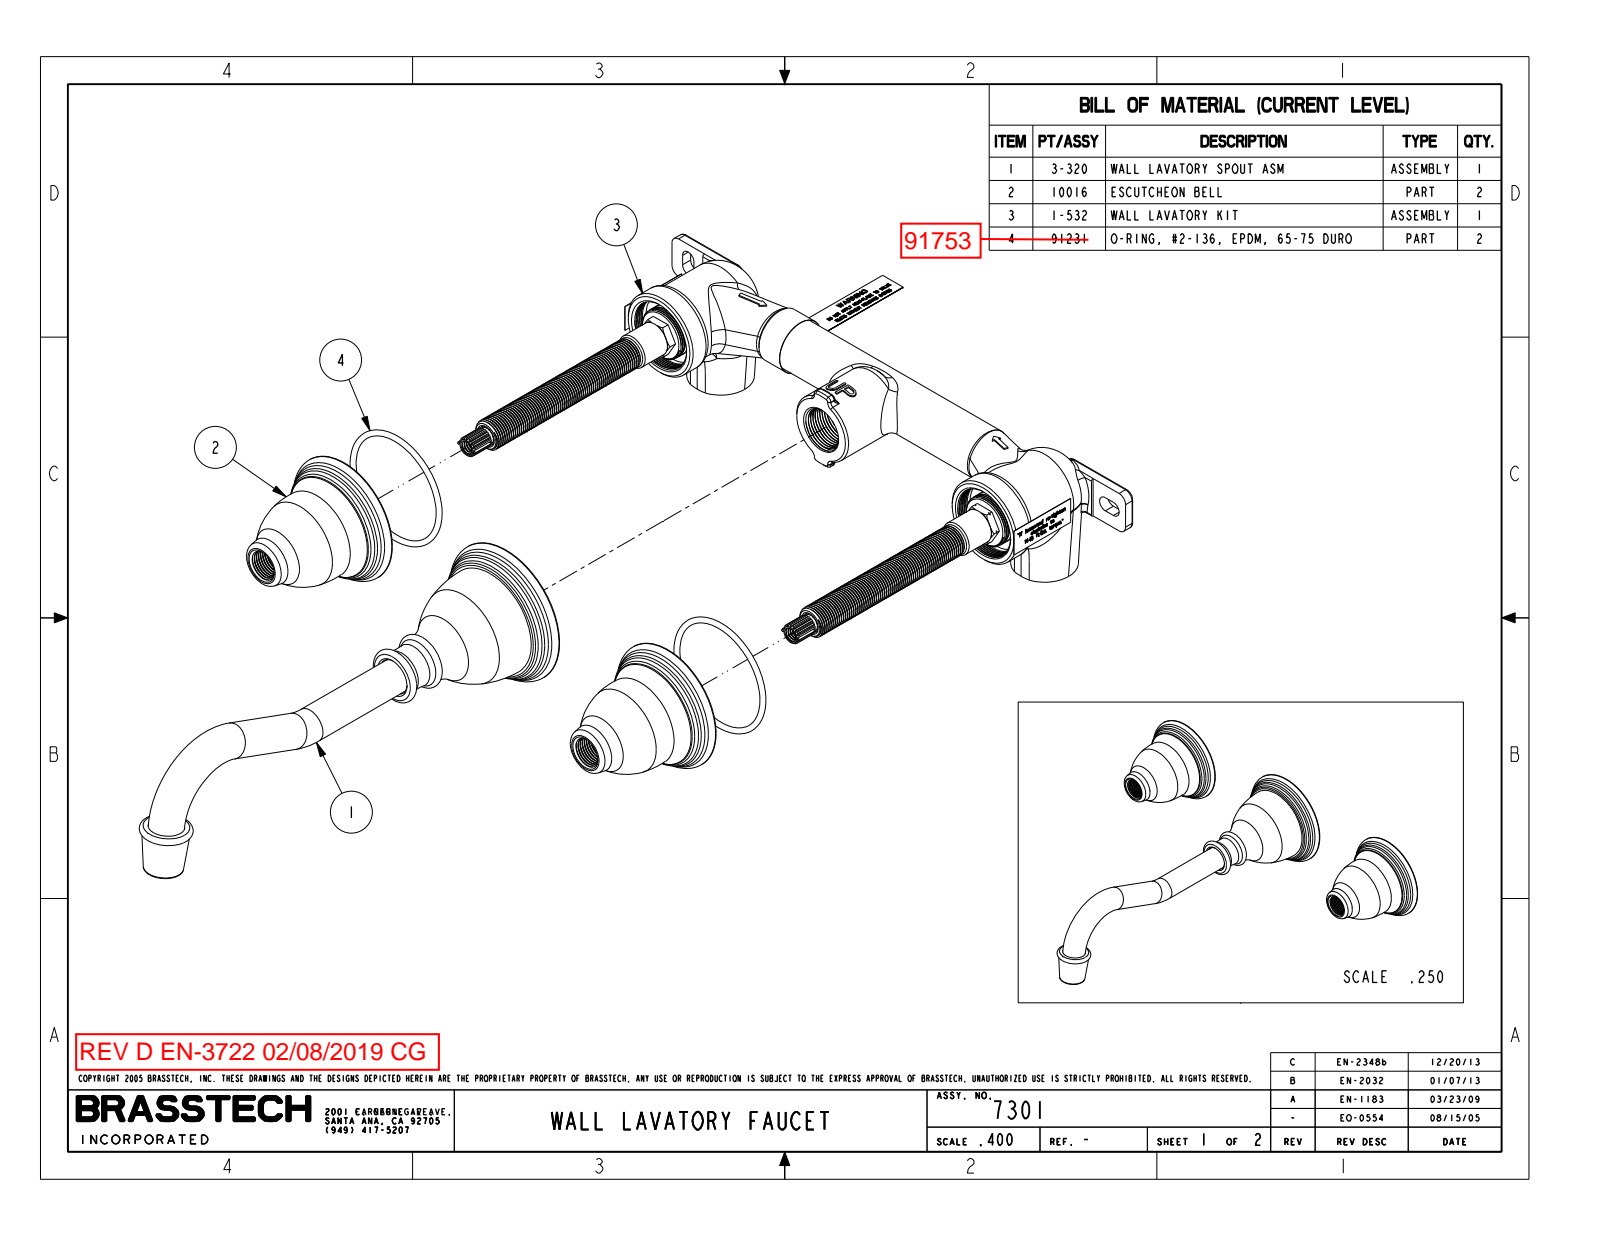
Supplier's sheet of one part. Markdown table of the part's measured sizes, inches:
| quantity | value |
| --- | --- |
| part name | 7301_WEB |
| STEP written by | PRO/ENGINEER BY PARAMETRIC TECHNOLOGY CORPORATION, 2009300 (CONFIG_CONTROL_DESIGN) |
| units | inches |
| bodies | 4 solids, 2038 faces (496 planar, 970 cylindrical, 572 other) |
| overall size | 12.586 × 10.34 × 3.03 |
| volume | 3.61 in³ |
| surface area | 208.9 in² |
| round holes (diameter × count) | 0.043 × 4, 0.315 × 3, 0.499 × 3, 0.406 × 2, 2.125 × 2, 0.354 × 1, 0.433 × 1, 0.44 × 1, 0.551 × 1, 0.56 × 1, 0.59 × 1, 0.597 × 1 |
| round bosses / shafts (diameter × count) | 2.34 × 2, 0.625 × 2, 0.585 × 2, 0.563 × 2, 0.201 × 2, 2.24 × 1, 0.97 × 1, 0.827 × 1 |
| partial cylindrical surfaces (radius × count) | 0.173 × 8, 0.164 × 2, 0.185 × 2, 0.128 × 1, 0.313 × 1 |
| main face-to-face distances | 1.353, 0.147, 0.08, 0.6, 0.753, 3.304, 3.904, 4.657, 0.52, 3.383 |
| hole center spacings | 0.19, 4, 4.19, 8, 8.19, 0.118, 0.19, 0.38 |
